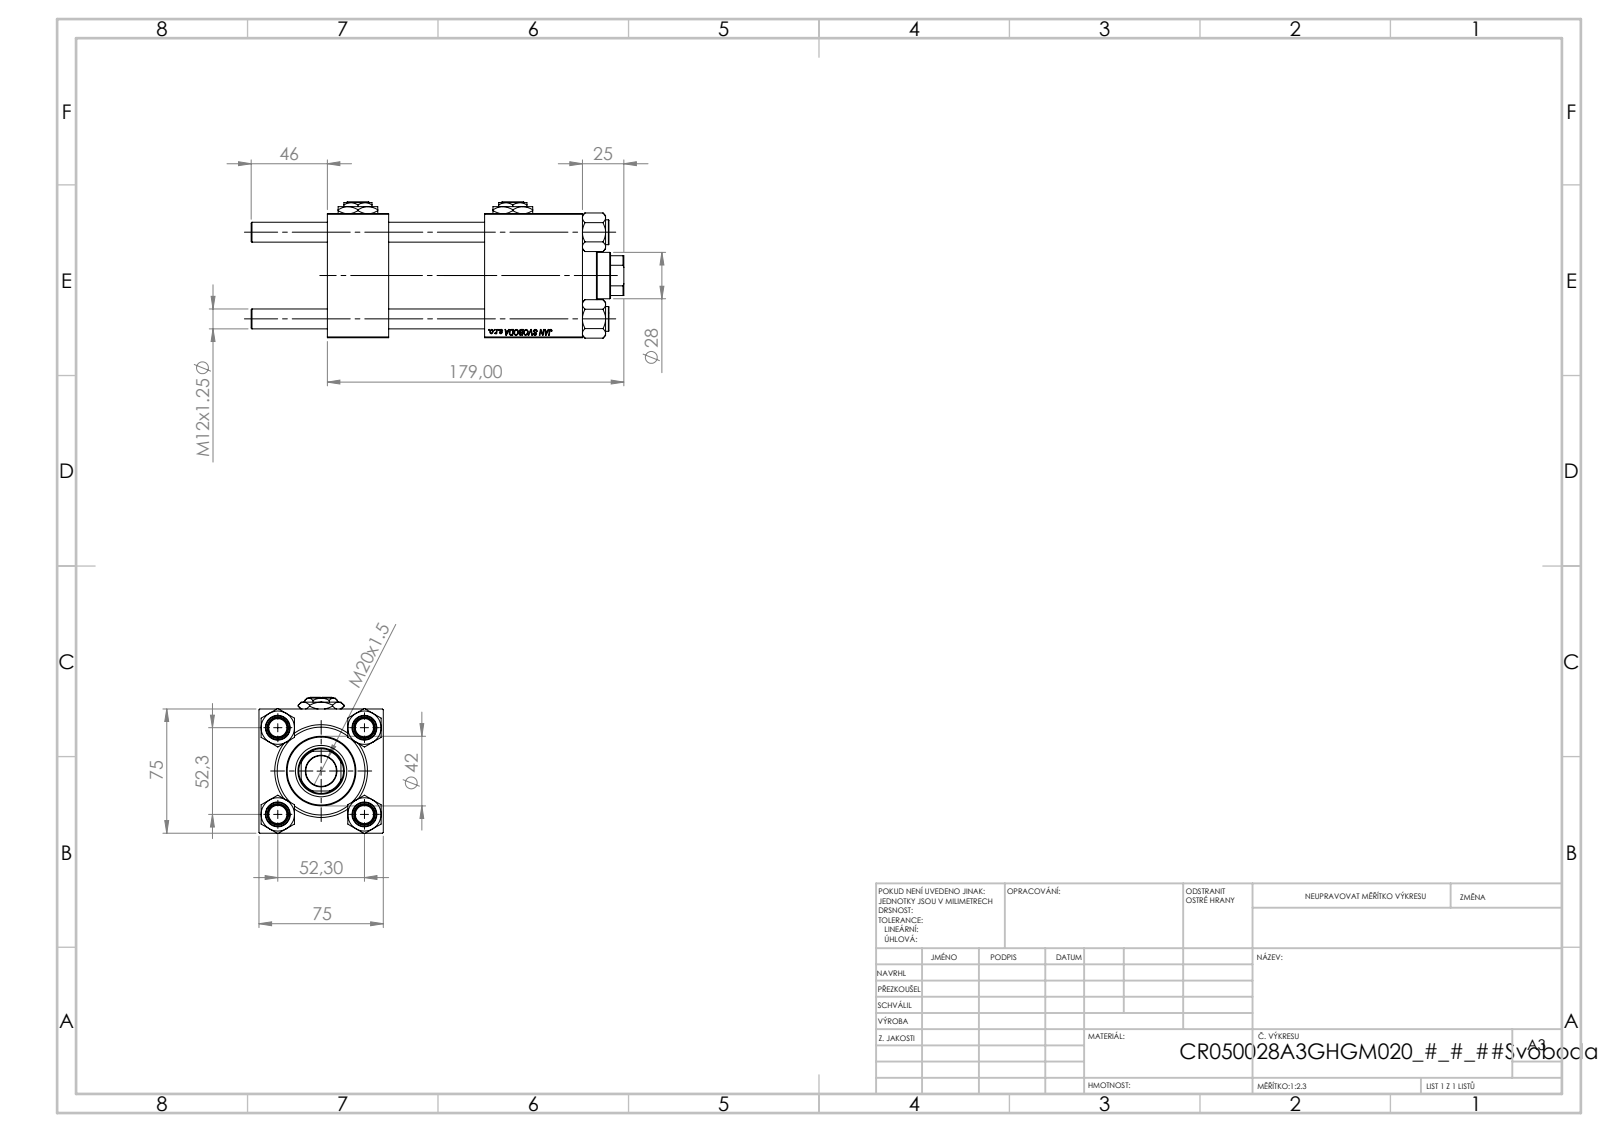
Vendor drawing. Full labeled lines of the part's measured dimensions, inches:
Part name (STEP PRODUCT): V215_VC_A; NUT_M5; Zatka_pro_OIL_PORT; V215CR_VCP (+2 more)
STEP written by: SolidWorks 2019 (CONFIG_CONTROL_DESIGN)
Units: inches
Bodies: 13 solids, 1233 faces (567 planar, 88 cylindrical, 578 other)
Overall size (bounding box): 8.858 × 3.239 × 2.953
Volume: 42.54 in³ · Surface area: 266.4 in²
Round holes (diameter × count): ⌀0.472 ×4, ⌀0.276 ×2, ⌀0.825 ×2, ⌀1.181 ×2, ⌀0.728 ×1, ⌀1.102 ×1, ⌀1.22 ×1, ⌀1.614 ×1, ⌀1.969 ×1, ⌀2.087 ×1
Round bosses / shafts (diameter × count): ⌀0.591 ×4, ⌀2.205 ×1, ⌀1.654 ×1
Partial cylindrical surfaces — rounded edges, fillets, slot ends (radius × count): R0.531 ×1
Main face-to-face distances: 2.953, 1.457, 6.063, 4.606, 3.74, 2.323, 2.283, 4.933, 3.476, 1.193
Hole centre spacings: 1.456, 2.059, 2.912, 3.681
